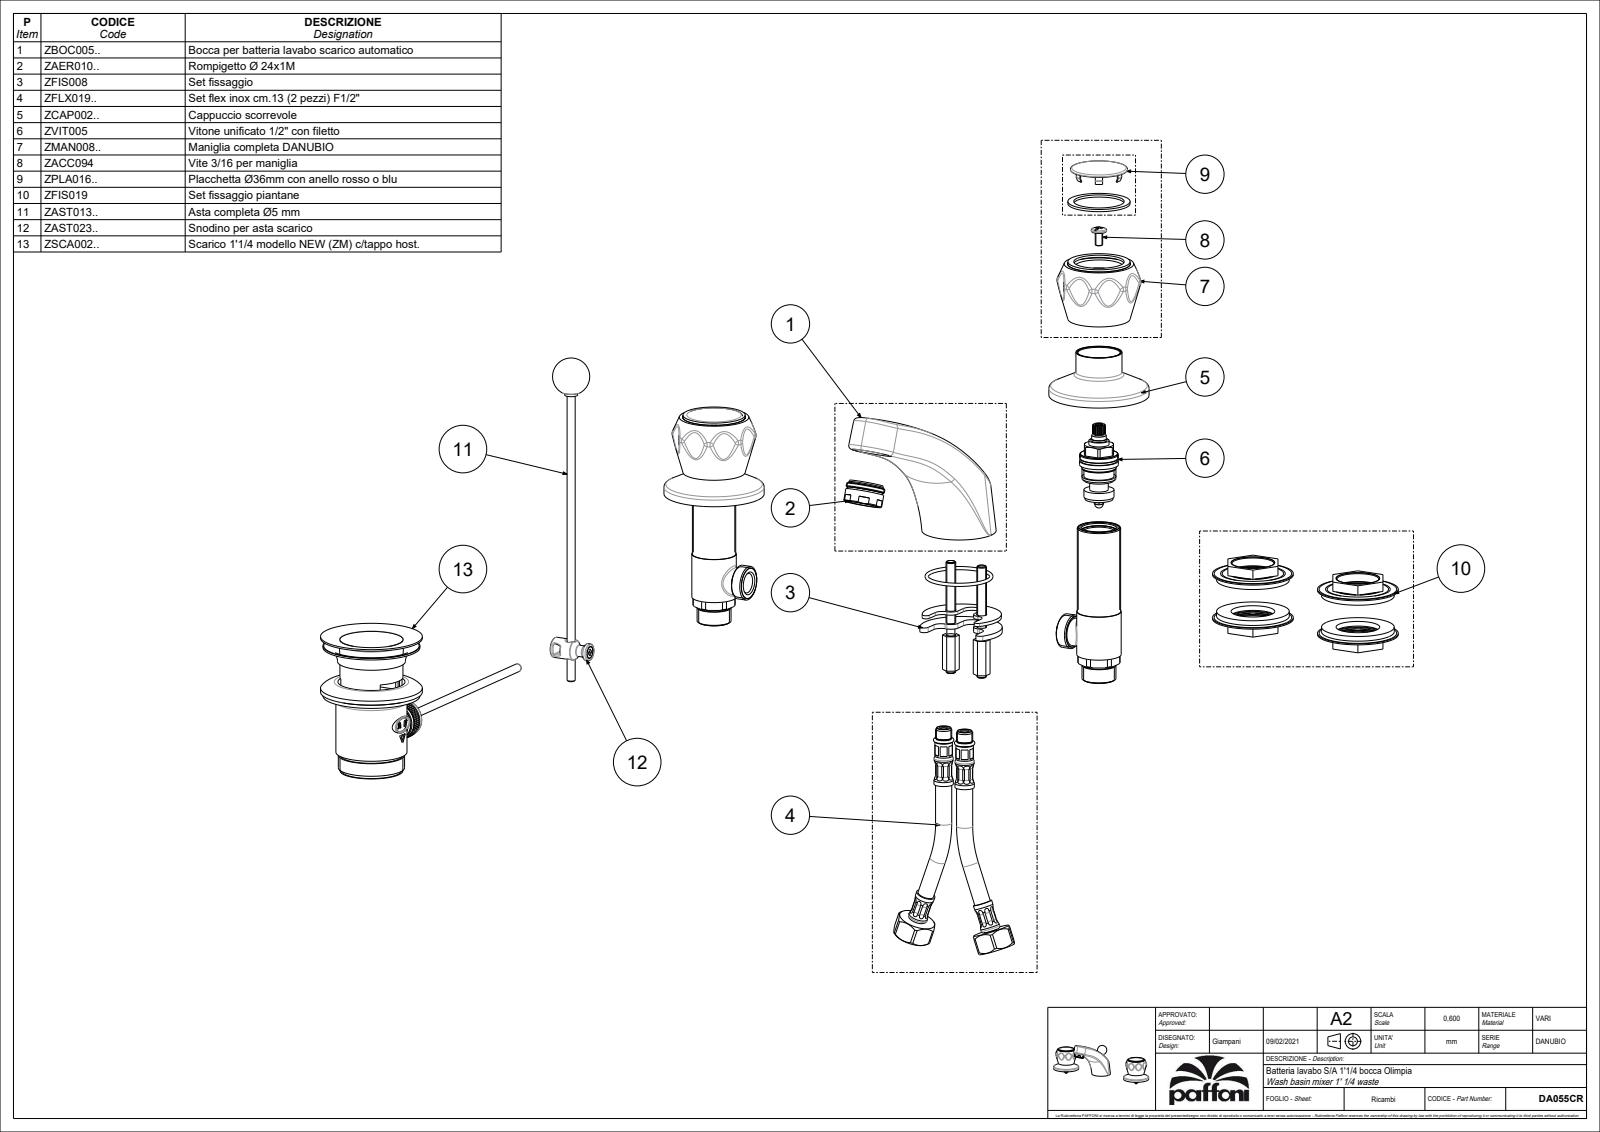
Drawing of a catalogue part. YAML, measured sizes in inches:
part_name: "DA055CR"
step_written_by: "CREO PARAMETRIC BY PTC INC, 2020044 (CONFIG_CONTROL_DESIGN)"
units: inches
bodies: {solids: 3, faces: 303, planar: 51, cylindrical: 72, other: 180}
overall_size: [10.315, 6.001, 3.858]
volume: 15.45
surface_area: 108
round_holes:
  - {diameter: 0.197, count: 2}
  - {diameter: 0.354, count: 2}
  - {diameter: 0.433, count: 2}
  - {diameter: 0.205, count: 1}
  - {diameter: 0.63, count: 1}
  - {diameter: 0.748, count: 1}
  - {diameter: 0.827, count: 1}
  - {diameter: 0.906, count: 1}
  - {diameter: 0.984, count: 1}
  - {diameter: 1.654, count: 1}
round_bosses_or_shafts:
  - {diameter: 2.441, count: 2}
  - {diameter: 1.516, count: 2}
  - {diameter: 1.496, count: 1}
  - {diameter: 0.937, count: 1}
  - {diameter: 0.866, count: 1}
  - {diameter: 0.315, count: 1}
  - {diameter: 0.197, count: 1}
partial_cylinders:
  - {radius: 0.839, count: 16}
  - {radius: 0.059, count: 4}
  - {radius: 0.197, count: 2}
  - {radius: 0.295, count: 2}
face_to_face_distances: [0.118, 0.543, 1.933, 1.39, 1.949, 1.406, 0.016, 0.394, 0.059, 1.89]
hole_center_spacings: [0.378, 0.461, 0.524, 0.559, 0.606, 0.938, 0.197, 0.591]
